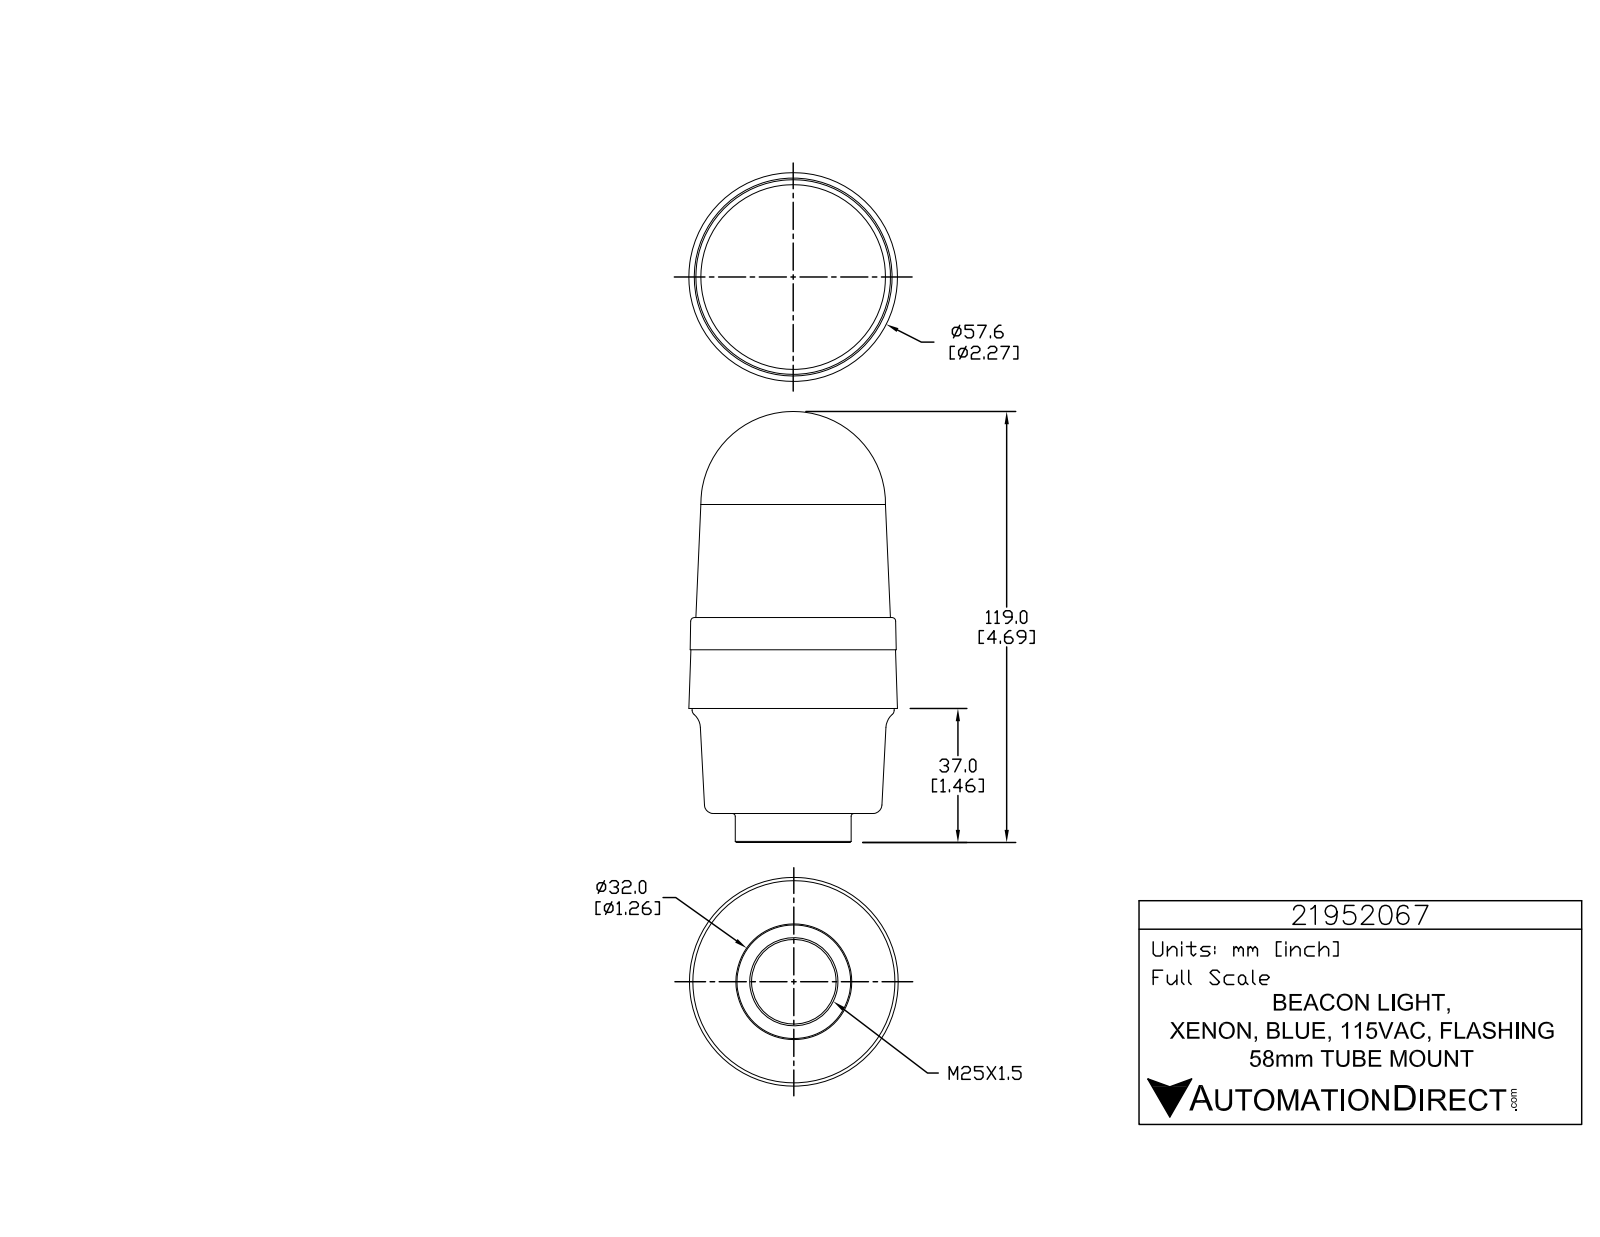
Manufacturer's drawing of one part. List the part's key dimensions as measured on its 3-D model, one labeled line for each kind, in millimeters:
Part name (STEP PRODUCT): 21952067
STEP written by: SolidWorks 2015 (AUTOMOTIVE_DESIGN)
Units: millimetres
Bodies: 1 solid, 791 faces (525 planar, 168 cylindrical, 98 other)
Overall size (bounding box): 119 × 57.6 × 57.6
Volume: 227 600 mm³ · Surface area: 21 970 mm²
Round holes (diameter × count): ⌀1 ×3, ⌀23.4 ×1
Round bosses / shafts (diameter × count): ⌀5.7 ×3, ⌀1.4 ×3, ⌀55.8 ×1, ⌀32 ×1
Partial cylindrical surfaces — rounded edges, fillets, slot ends (radius × count): R0.2 ×6, R0.2 ×6, R0.2 ×6, R3.3 ×6, R0.1 ×3, R0.1 ×3, R0.2 ×3, R0.2 ×3
Main face-to-face distances: 8, 29, 37, 25.1, 54.1, 62.1, 8.9, 16.2, 45.2, 53.2
